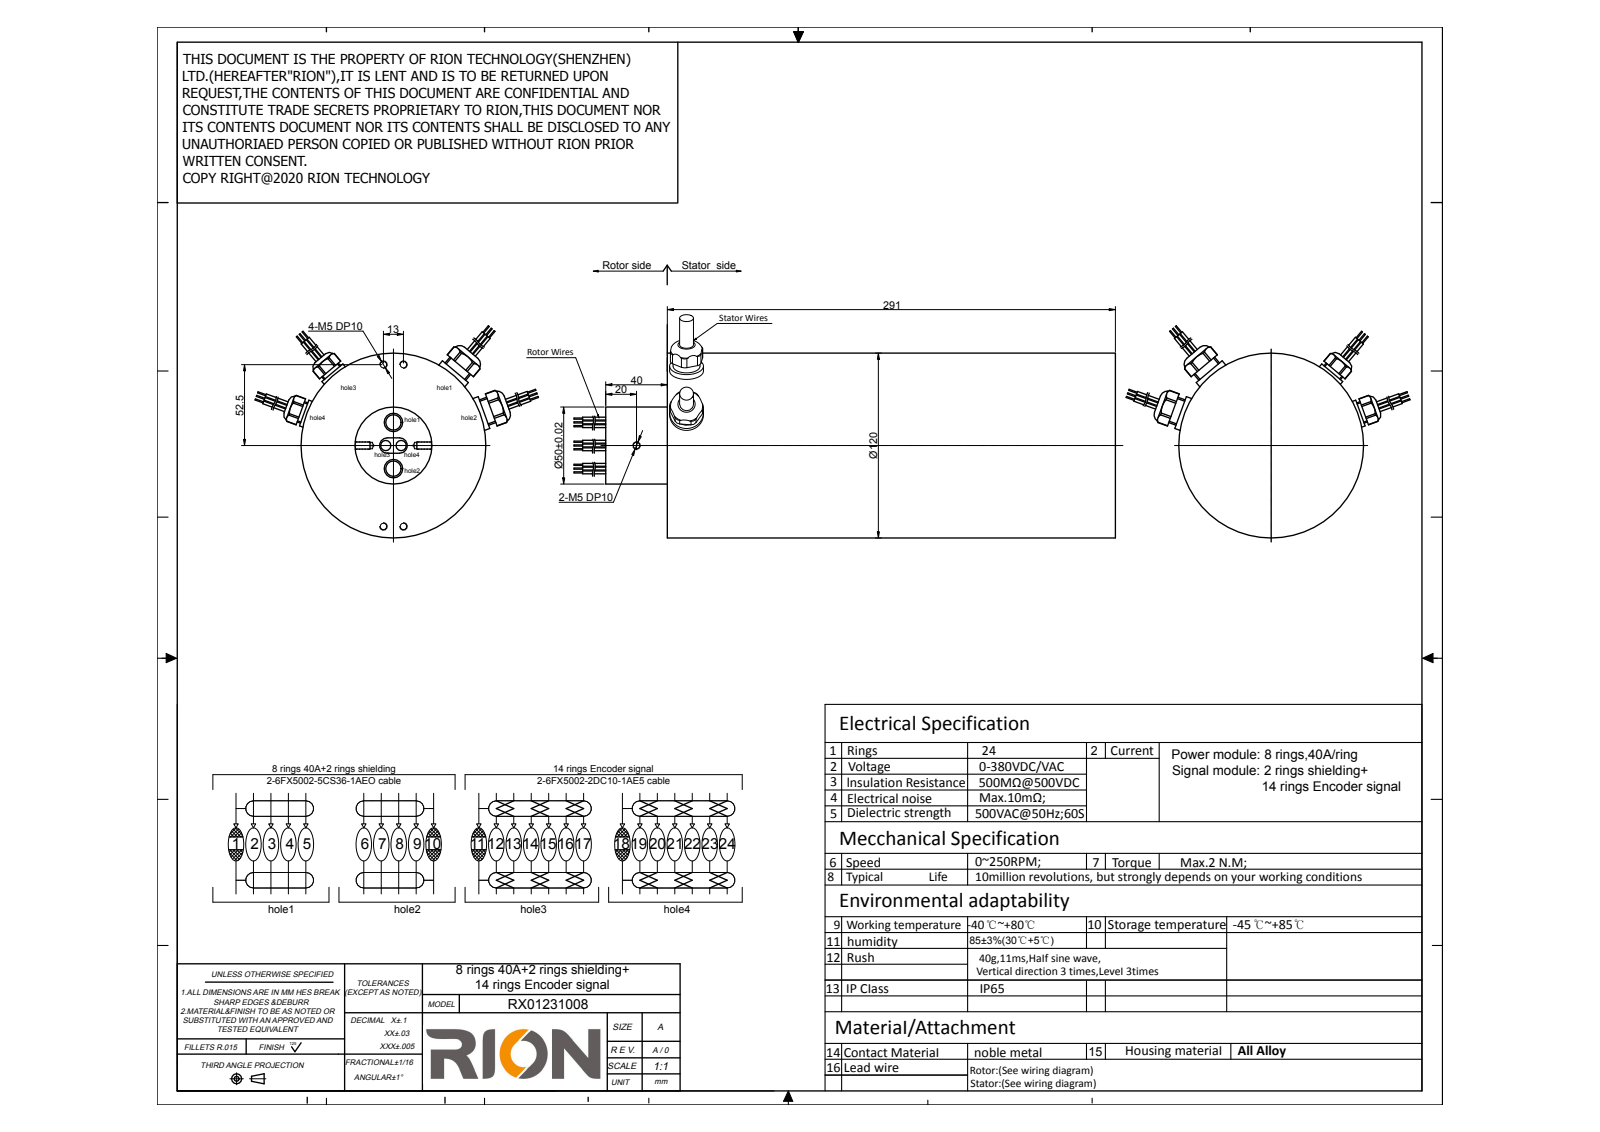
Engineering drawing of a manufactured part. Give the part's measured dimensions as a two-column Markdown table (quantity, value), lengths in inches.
| quantity | value |
| --- | --- |
| part name | RX01231008-RZ099-P0840-S16-IP65 |
| STEP written by | SolidWorks 2014 (CONFIG_CONTROL_DESIGN) |
| units | inches |
| bodies | 3 solids, 181 faces (98 planar, 63 cylindrical, 20 other) |
| overall size | 13.819 × 7.128 × 5.332 |
| volume | 206.9 in³ |
| surface area | 230.8 in² |
| round holes (diameter × count) | 0.165 × 5, 0.472 × 2 |
| round bosses / shafts (diameter × count) | 0.551 × 6, 0.7 × 4, 0.354 × 4, 0.394 × 2, 0.264 × 2, 4.724 × 1, 1.969 × 1 |
| partial cylindrical surfaces (radius × count) | 0.197 × 2 |
| main face-to-face distances | 11.457, 1.575, 13.031, 0.551, 0.787, 2.362, 13.819, 0.291, 0.866, 0.079 |
| hole center spacings | 1.498, 2.67, 0.512, 4.134, 4.165, 1.181 |
